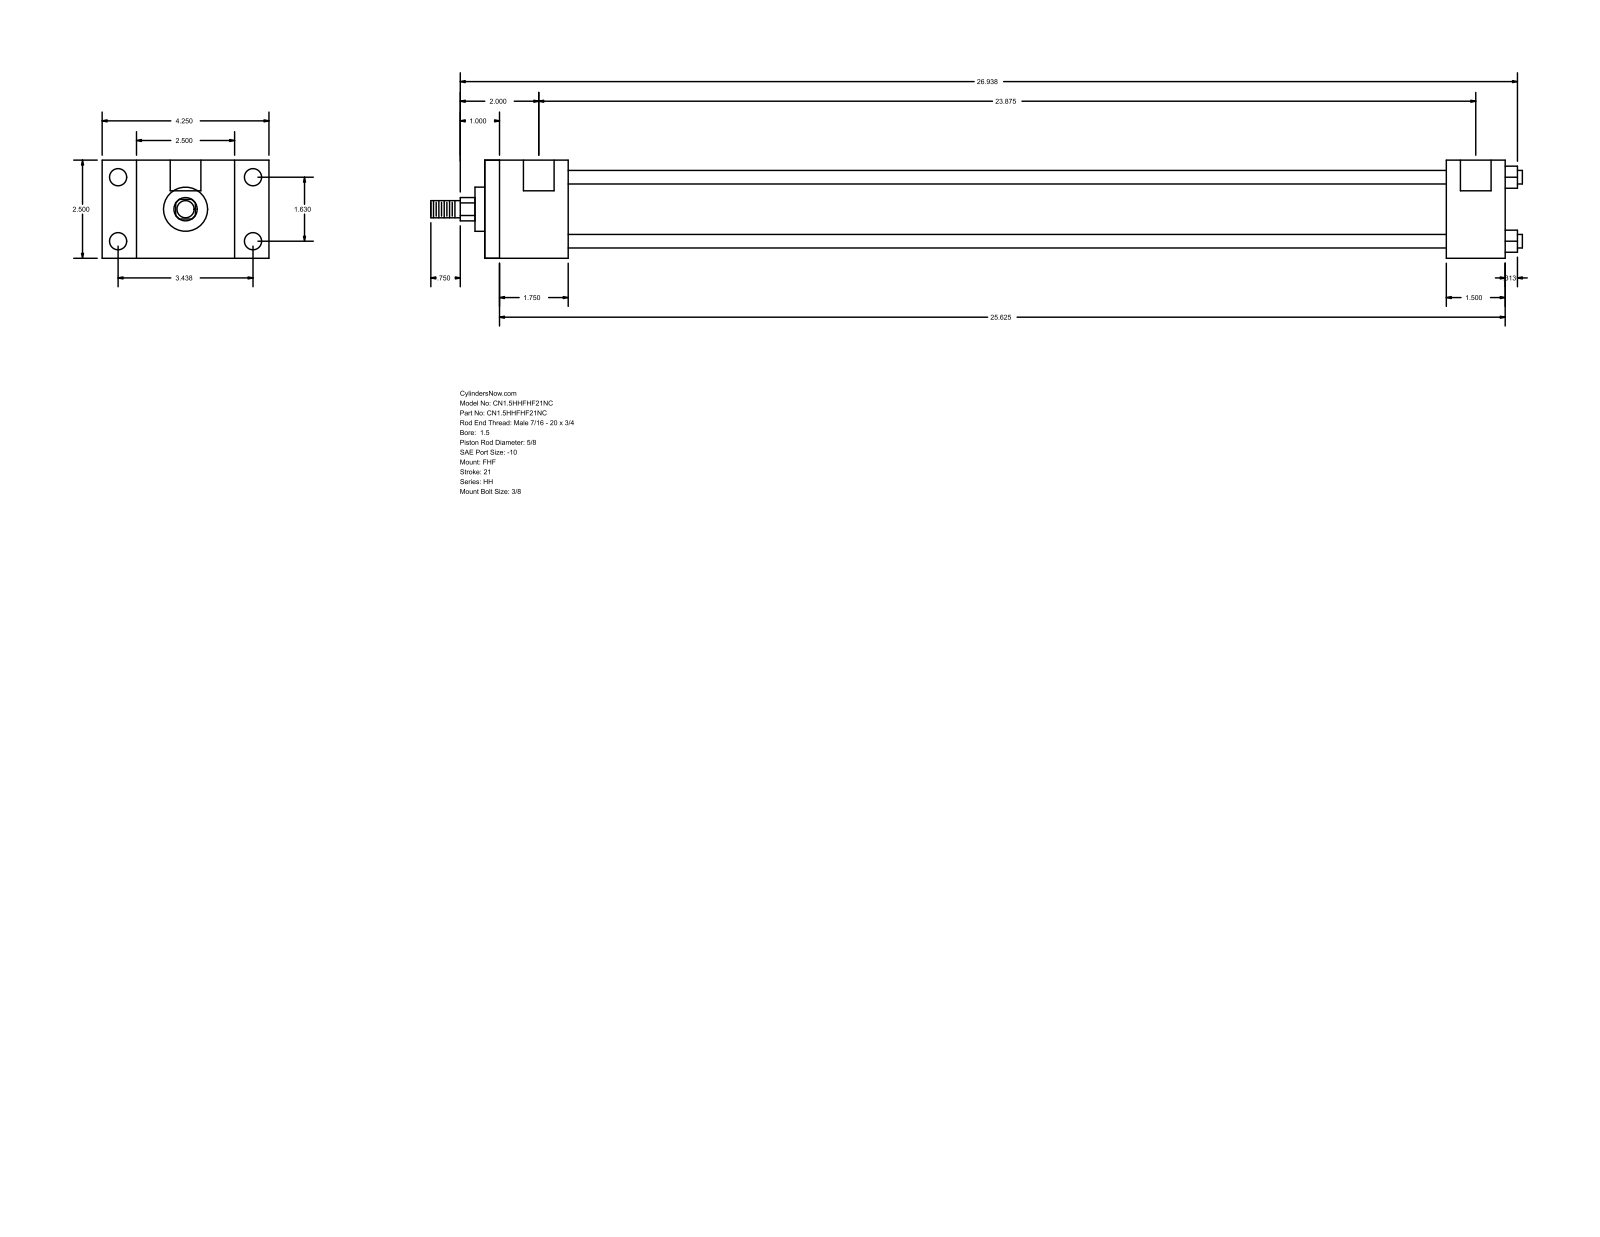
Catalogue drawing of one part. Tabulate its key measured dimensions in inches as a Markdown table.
| quantity | value |
| --- | --- |
| part name | HH_FHF__0150_0.625 |
| STEP written by | GSSL Pune (CONFIG_CONTROL_DESIGN) |
| units | inches |
| bodies | 0 solids, 88 faces (60 planar, 28 cylindrical, 0 other) |
| overall size | 27.813 × 4.25 × 2.5 |
| round holes (diameter × count) | 0.219 × 4, 0.438 × 4, 0.781 × 2 |
| round bosses / shafts (diameter × count) | 0.345 × 4, 1.75 × 1, 1.125 × 1, 0.625 × 1, 0.437 × 1 |
| partial cylindrical surfaces (radius × count) | 0.297 × 1 |
| main face-to-face distances | 2.5, 0.875, 3.375, 2.125, 4.25, 26, 23.875, 1.5, 24.5, 22.375 |
| hole center spacings | 1.63, 3.438, 3.805, 24, 0.062, 0.063, 23.875, 23.937 |
